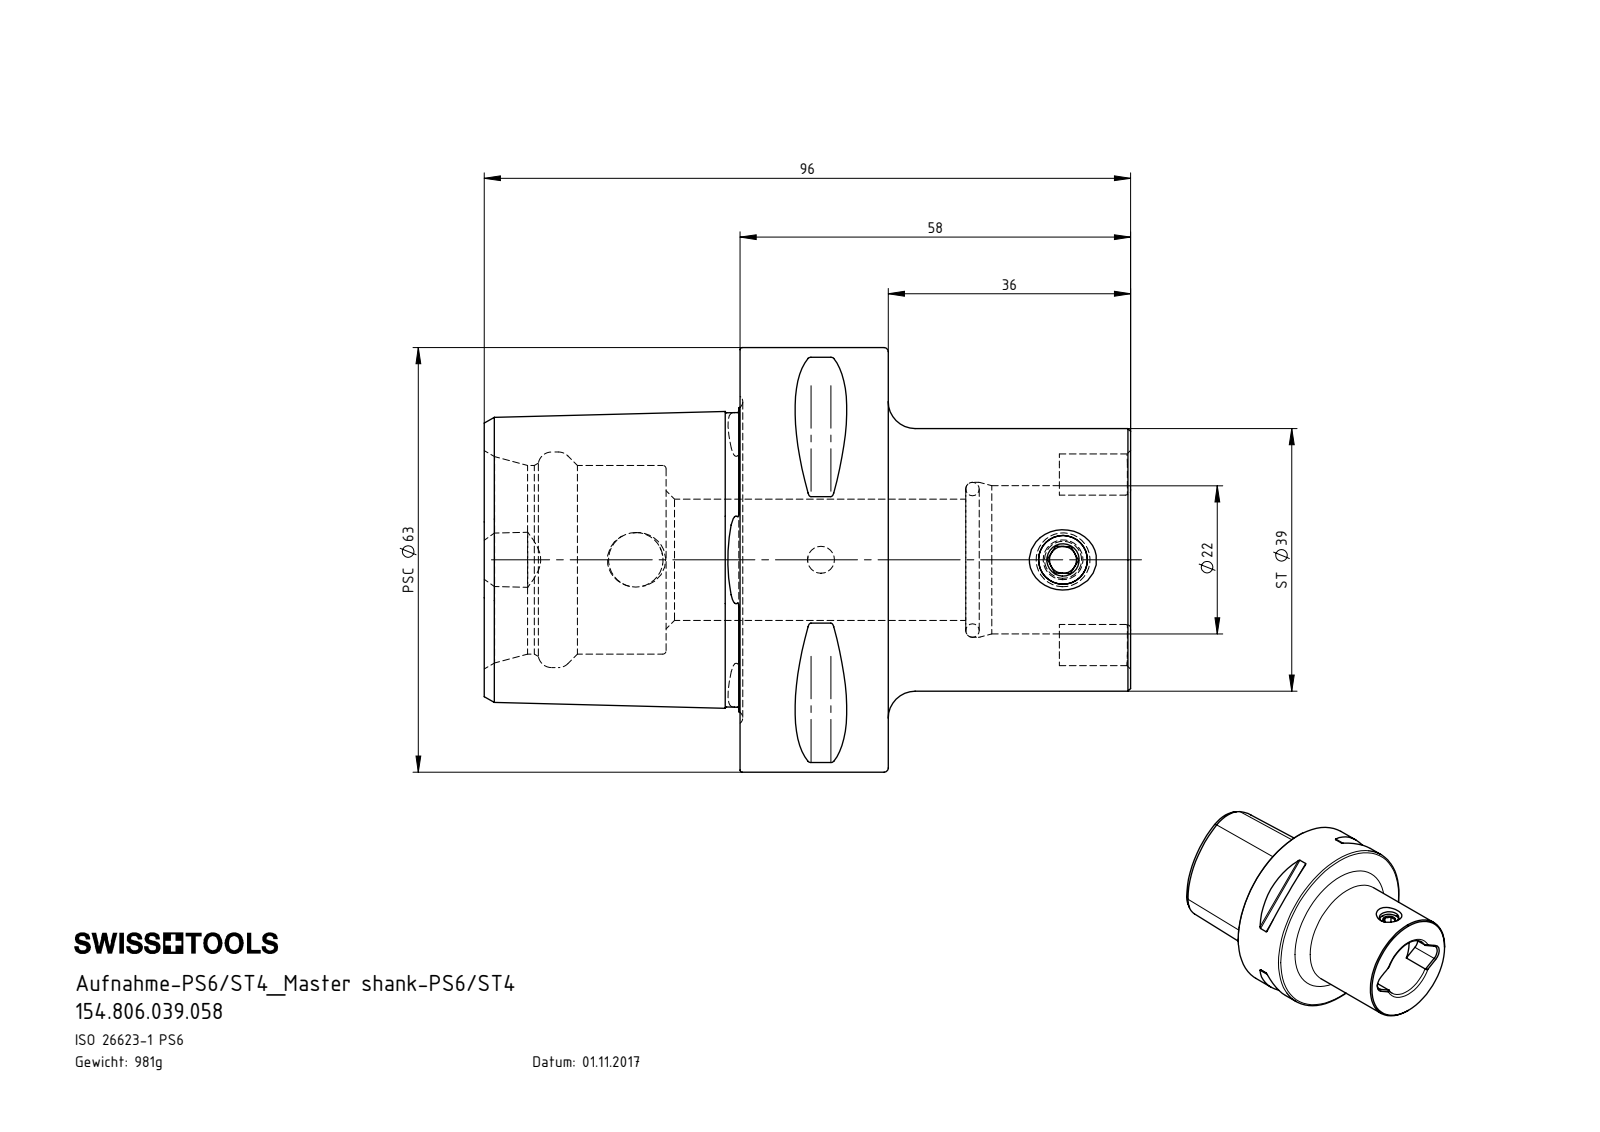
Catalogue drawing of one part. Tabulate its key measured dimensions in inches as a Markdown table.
| quantity | value |
| --- | --- |
| part name | ST4-ER1.001.011_A; PS6.ST4.K01.058; PS6-ST4.K01.058_B; DIN 3771 - 19x2 |
| STEP written by | SolidWorks 2017 (AUTOMOTIVE_DESIGN) |
| units | inches |
| bodies | 3 solids, 131 faces (43 planar, 25 cylindrical, 63 other) |
| overall size | 3.78 × 2.48 × 2.48 |
| volume | 7.638 in³ |
| surface area | 42.36 in² |
| round holes (diameter × count) | 0.157 × 2, 0.285 × 1, 0.319 × 1, 0.709 × 1, 0.866 × 1, 0.906 × 1, 1.102 × 1, 1.26 × 1 |
| round bosses / shafts (diameter × count) | 2.48 × 1, 1.535 × 1, 0.315 × 1 |
| partial cylindrical surfaces (radius × count) | 0.02 × 8, 0.126 × 2, 0.236 × 1 |
| main face-to-face distances | 0.866, 2.283, 1.417, 1.496, 2.362, 3.78, 0.98, 0.433, 1.063, 1.299 |
| hole center spacings | 1.083, 1.415, 2.498 |
